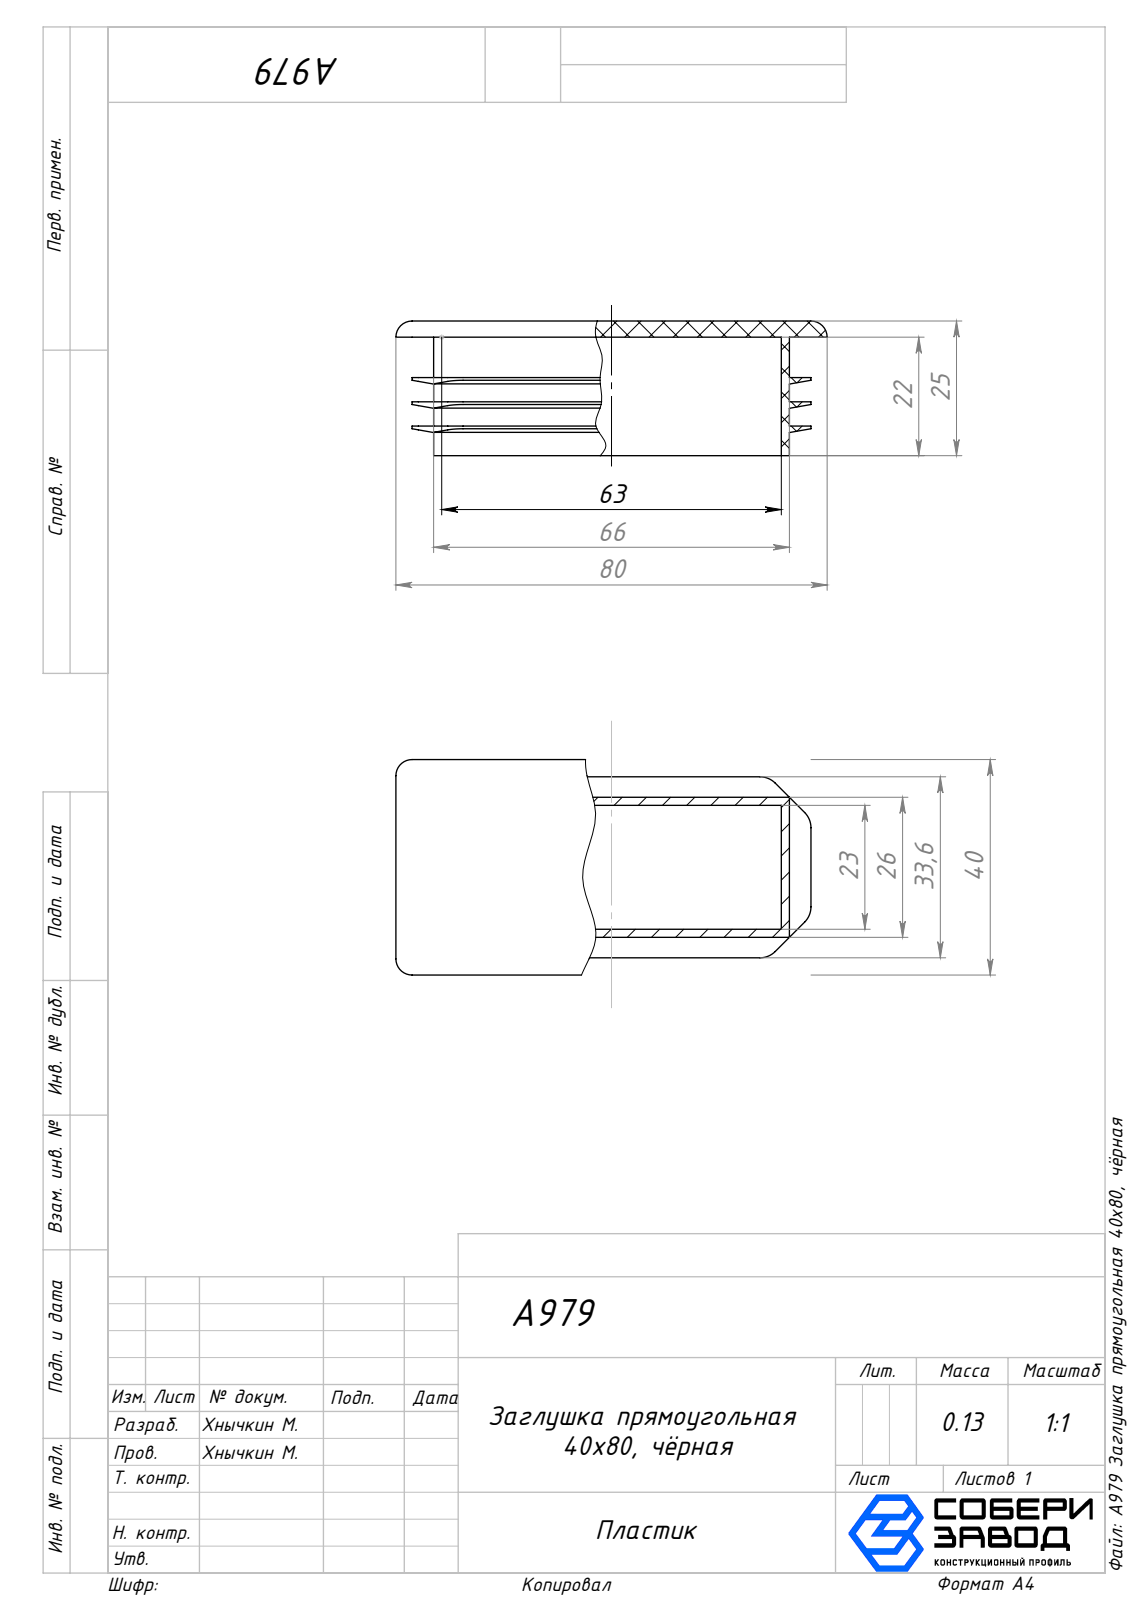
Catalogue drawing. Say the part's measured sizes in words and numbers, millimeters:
The part is named "A979 Заглушка прямоугольная 40х80, чёрная". Its 3-D file was written by "SolidWorks 2025 (AUTOMOTIVE_DESIGN)". It is 1 solid with 104 faces: 72 planar, 28 cylindrical and 4 other. Overall it measures 80 by 40 by 25 millimeters. Its volume is 16 656 cubic millimeters and its surface area 18 209 square millimeters. Partial cylindrical surfaces (rounded edges, fillets, slot ends): 8 of radius 4, 4 of radius 3. The main face-to-face distances are 1.5, 3, 24.5, 23, 4.5, 26, 4.43, 64.5, 9, 16.5.
